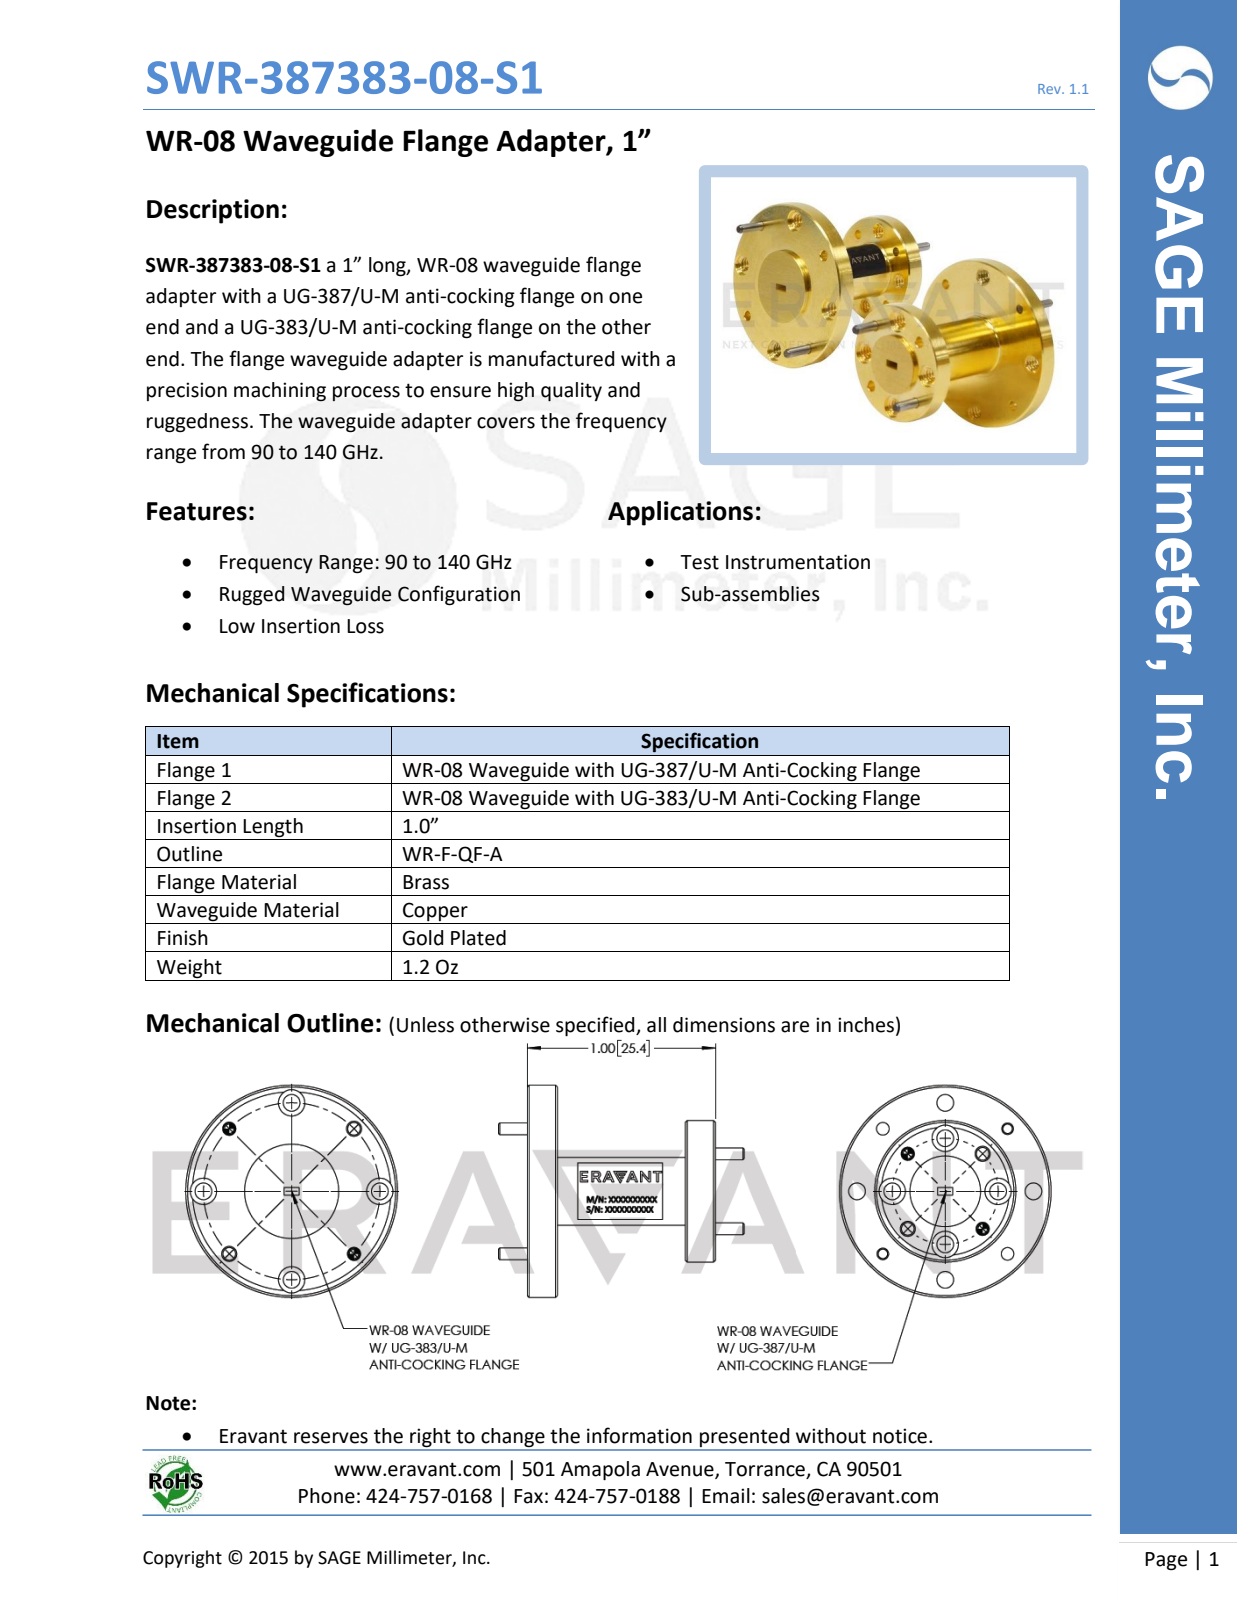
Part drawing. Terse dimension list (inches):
name: SWR-387383-08-S1
written by: SolidWorks 2016 (CONFIG_CONTROL_DESIGN)
unit: in
bodies: 5 solids, 138 faces (32 planar, 66 cylindrical, 40 other)
size: 1.305 × 1.125 × 1.125
volume: 0.263 in³; area: 4.867 in²
holes: 8× ⌀0.089, 8× ⌀0.14, 4× ⌀0.06, 4× ⌀0.067
bosses: 4× ⌀0.063, 1× ⌀1.125, 1× ⌀0.75, 1× ⌀0.5, 1× ⌀0.375, 1× ⌀0.375
face distances: 0.13, 0.03, 0.97, 0.81, 0.68, 0.94, 0.81, 0.13, 0.16, 0.84
hole spacings: 0.335, 0.547, 0.697, 0.215, 0.359, 0.663, 0.866, 0.398
